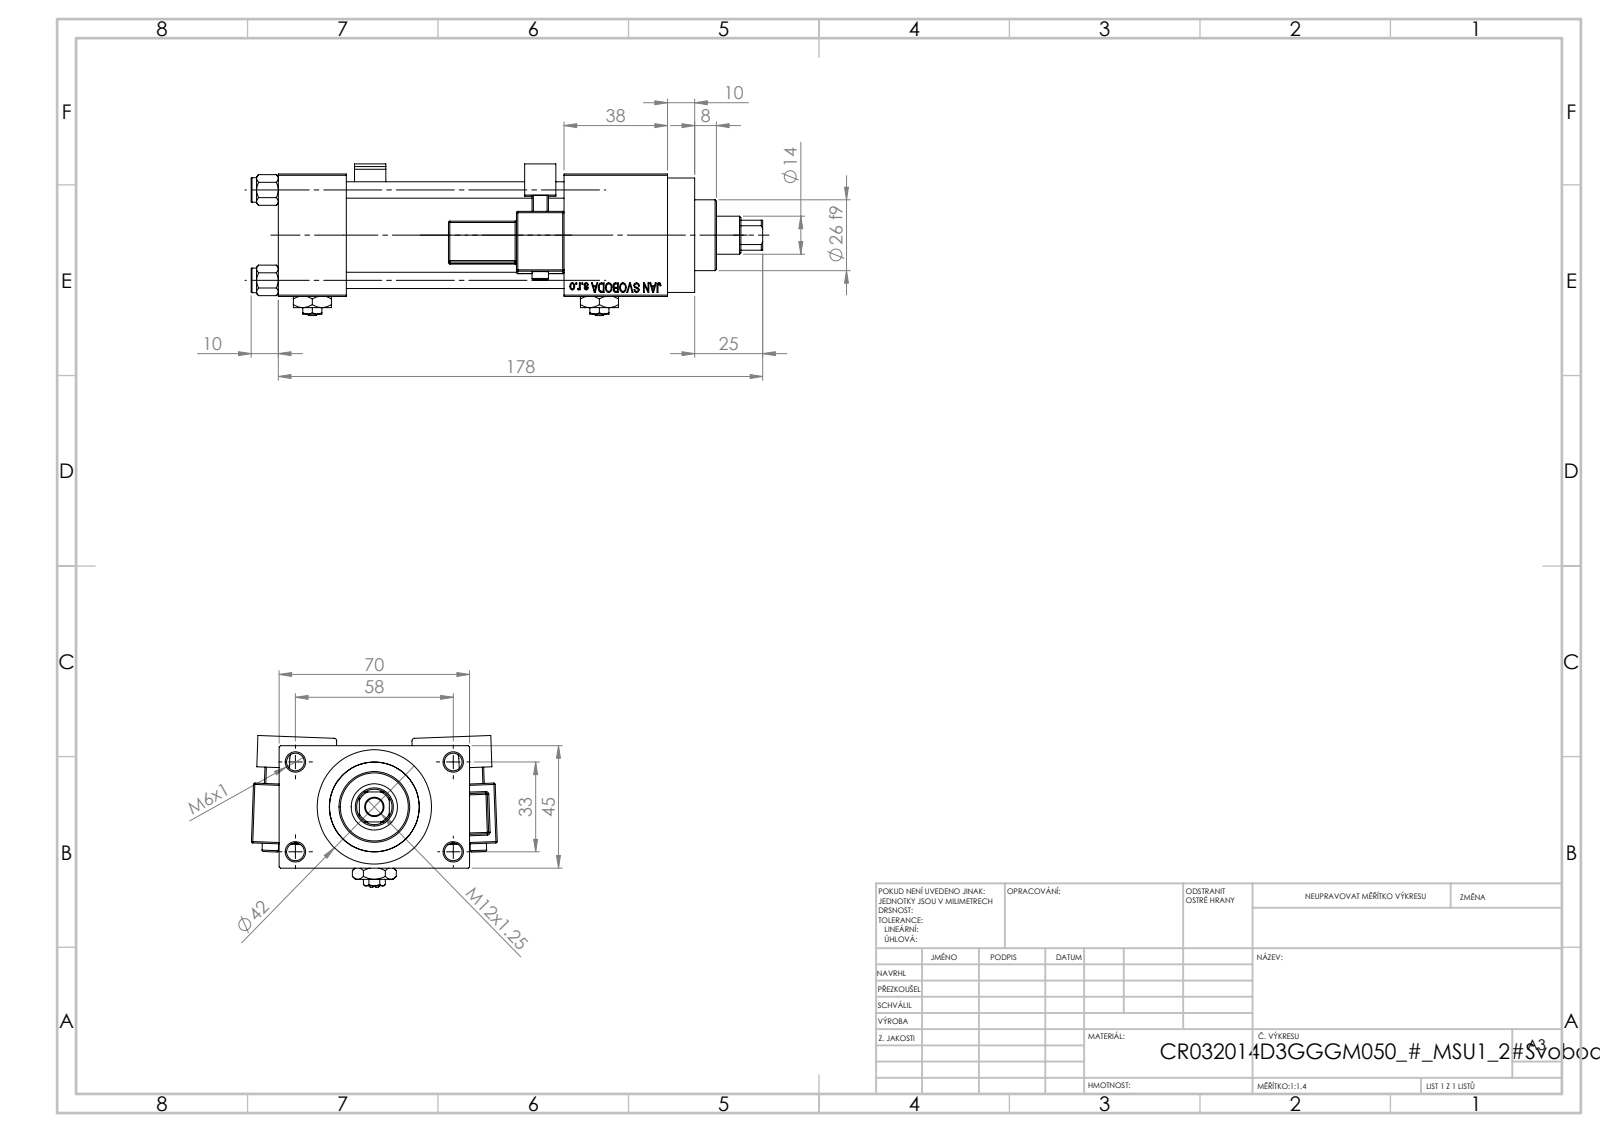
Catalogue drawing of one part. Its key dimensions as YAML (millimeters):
part_name: "V215CR_D_Body; V215_VC_A; V215CR_MSU; Zatka_pro_OIL_PORT (+3 more)"
step_written_by: "SolidWorks 2019 (CONFIG_CONTROL_DESIGN)"
units: millimeters
bodies: {solids: 15, faces: 1360, planar: 604, cylindrical: 160, other: 596}
overall_size: [188, 90.31, 55.72]
volume: 289263
surface_area: 98796
round_holes:
  - {diameter: 6.5, count: 5}
  - {diameter: 6, count: 4}
  - {diameter: 7, count: 2}
  - {diameter: 13.16, count: 2}
  - {diameter: 20, count: 2}
  - {diameter: 14, count: 1}
  - {diameter: 17, count: 1}
  - {diameter: 24, count: 1}
  - {diameter: 32, count: 1}
  - {diameter: 33, count: 1}
round_bosses_or_shafts:
  - {diameter: 9, count: 4}
  - {diameter: 6, count: 2}
  - {diameter: 42, count: 1}
  - {diameter: 38, count: 1}
  - {diameter: 26, count: 1}
partial_cylinders:
  - {radius: 0.5, count: 48}
  - {radius: 1, count: 2}
  - {radius: 2.5, count: 2}
  - {radius: 4, count: 2}
  - {radius: 6.5, count: 1}
face_to_face_distances: [45, 25, 12.5, 80, 3, 57.5, 105, 118, 38, 70]
hole_center_spacings: [12.4, 23.48, 33.2, 33.37, 35.35, 45.6, 56.35, 33]
